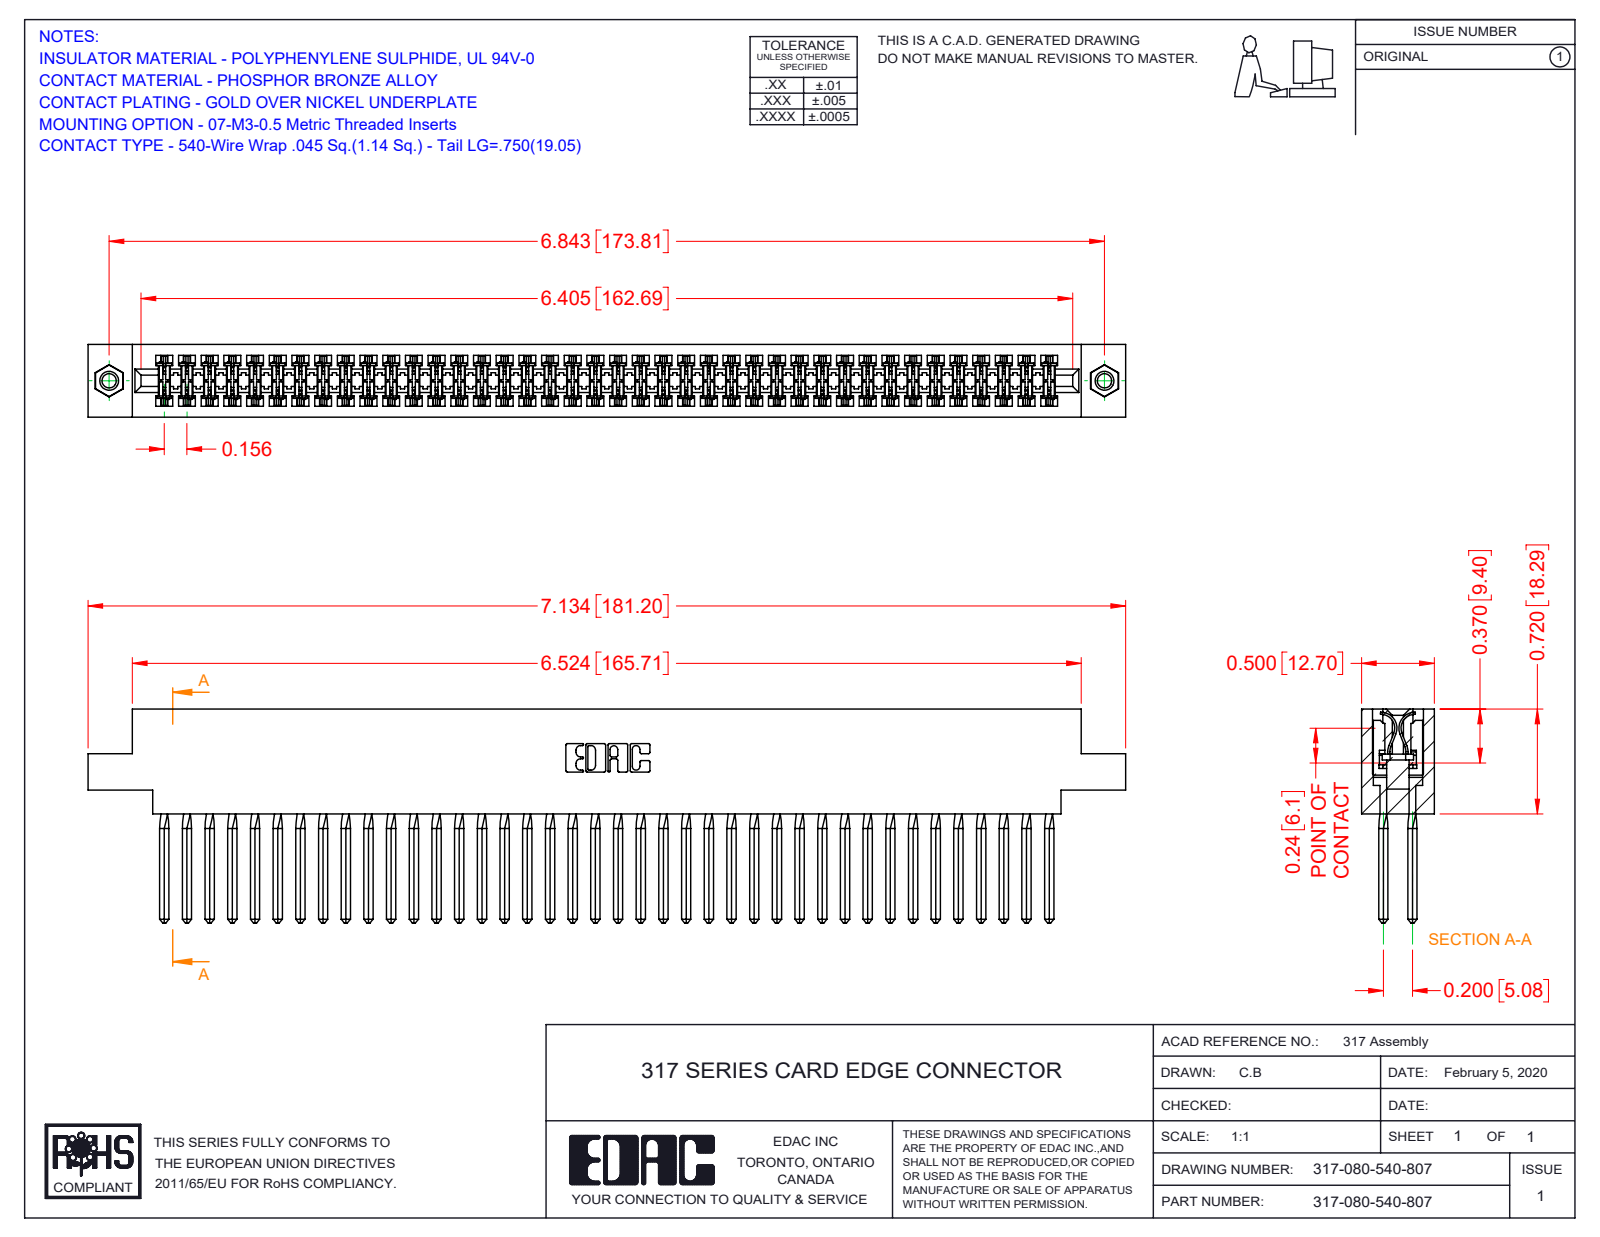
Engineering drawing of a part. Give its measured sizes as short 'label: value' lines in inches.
name: 317-080-540-807; 317 Part_.156 Dia - TI; 345-250-001_345-250-005-103; 317-290-001_540
written by: SolidWorks 2016 (CONFIG_CONTROL_DESIGN)
unit: in
bodies: 83 solids, 7282 faces (5930 planar, 1016 cylindrical, 336 other)
size: 7.134 × 1.47 × 0.5
volume: 1.851 in³; area: 70.03 in²
holes: 2× ⌀0.098, 2× ⌀0.125, 2× ⌀0.156
bosses: 2× ⌀0.155
rounds: 160× R0.015, 22× R0.01, 6× R0.007, 6× R0.031, 3× R0.026, 2× R0.095, 2× R0.1, 2× R0.11
face distances: 0.5, 0.075, 0.425, 0.35, 0.195, 0.094, 0.2, 0.115, 0.131, 0.11
hole spacings: 6.843
